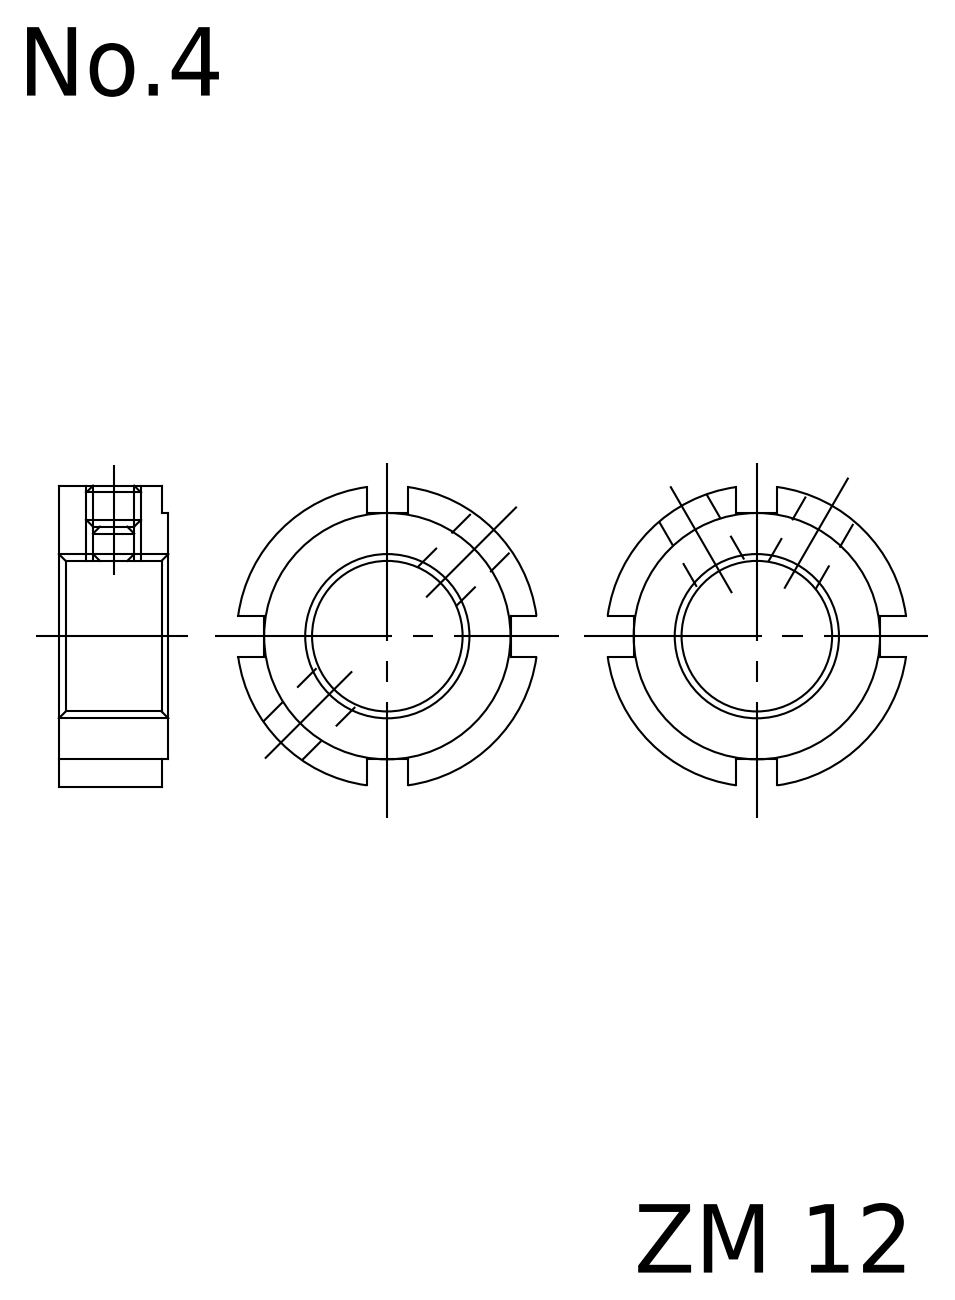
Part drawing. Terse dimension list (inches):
name: FKD ZM 12
written by: Autodesk Inventor 2011 (AUTOMOTIVE_DESIGN)
unit: in
bodies: 1 solid, 26 faces (18 planar, 8 cylindrical, 0 other)
size: 0.858 × 0.858 × 0.315
volume: 0.111 in³; area: 2.353 in²
holes: 2× ⌀0.128, 1× ⌀0.472
bosses: 1× ⌀0.866, 1× ⌀0.709
face distances: 0.295, 0.315, 0.02, 0.413, 0.118, 0.709
